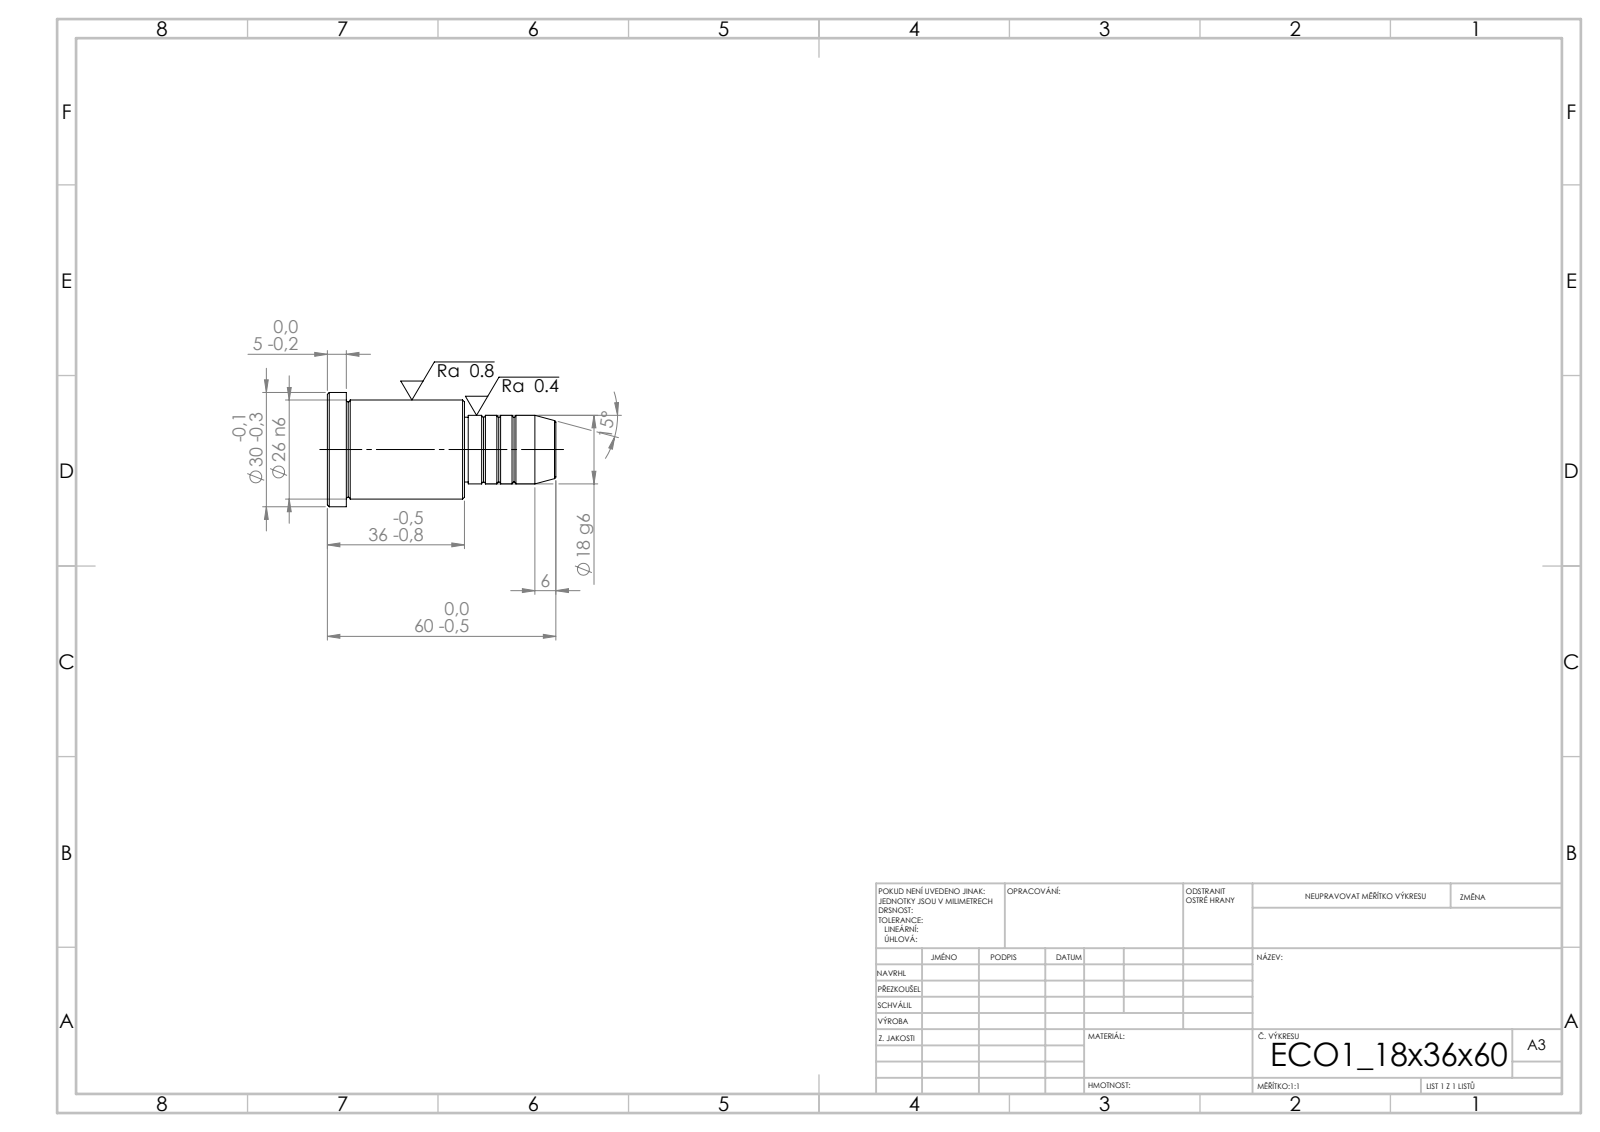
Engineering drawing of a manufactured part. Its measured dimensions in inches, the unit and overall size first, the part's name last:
Units: inches
Overall size (bounding box): 2.362 × 1.181 × 1.181
Round bosses / shafts (diameter × count): ⌀1.181 ×1, ⌀1.024 ×1, ⌀0.709 ×1, ⌀0.669 ×1
Main face-to-face distances: 1.417, 1.22, 0.197, 0.945, 2.165, 2.362, 0.906, 0.039, 1.26, 1.457
Volume: 1.571 in³ · Surface area: 9.001 in²
Bodies: 1 solid, 43 faces (5 planar, 14 cylindrical, 24 other)
STEP written by: SolidWorks 2019 (CONFIG_CONTROL_DESIGN)
